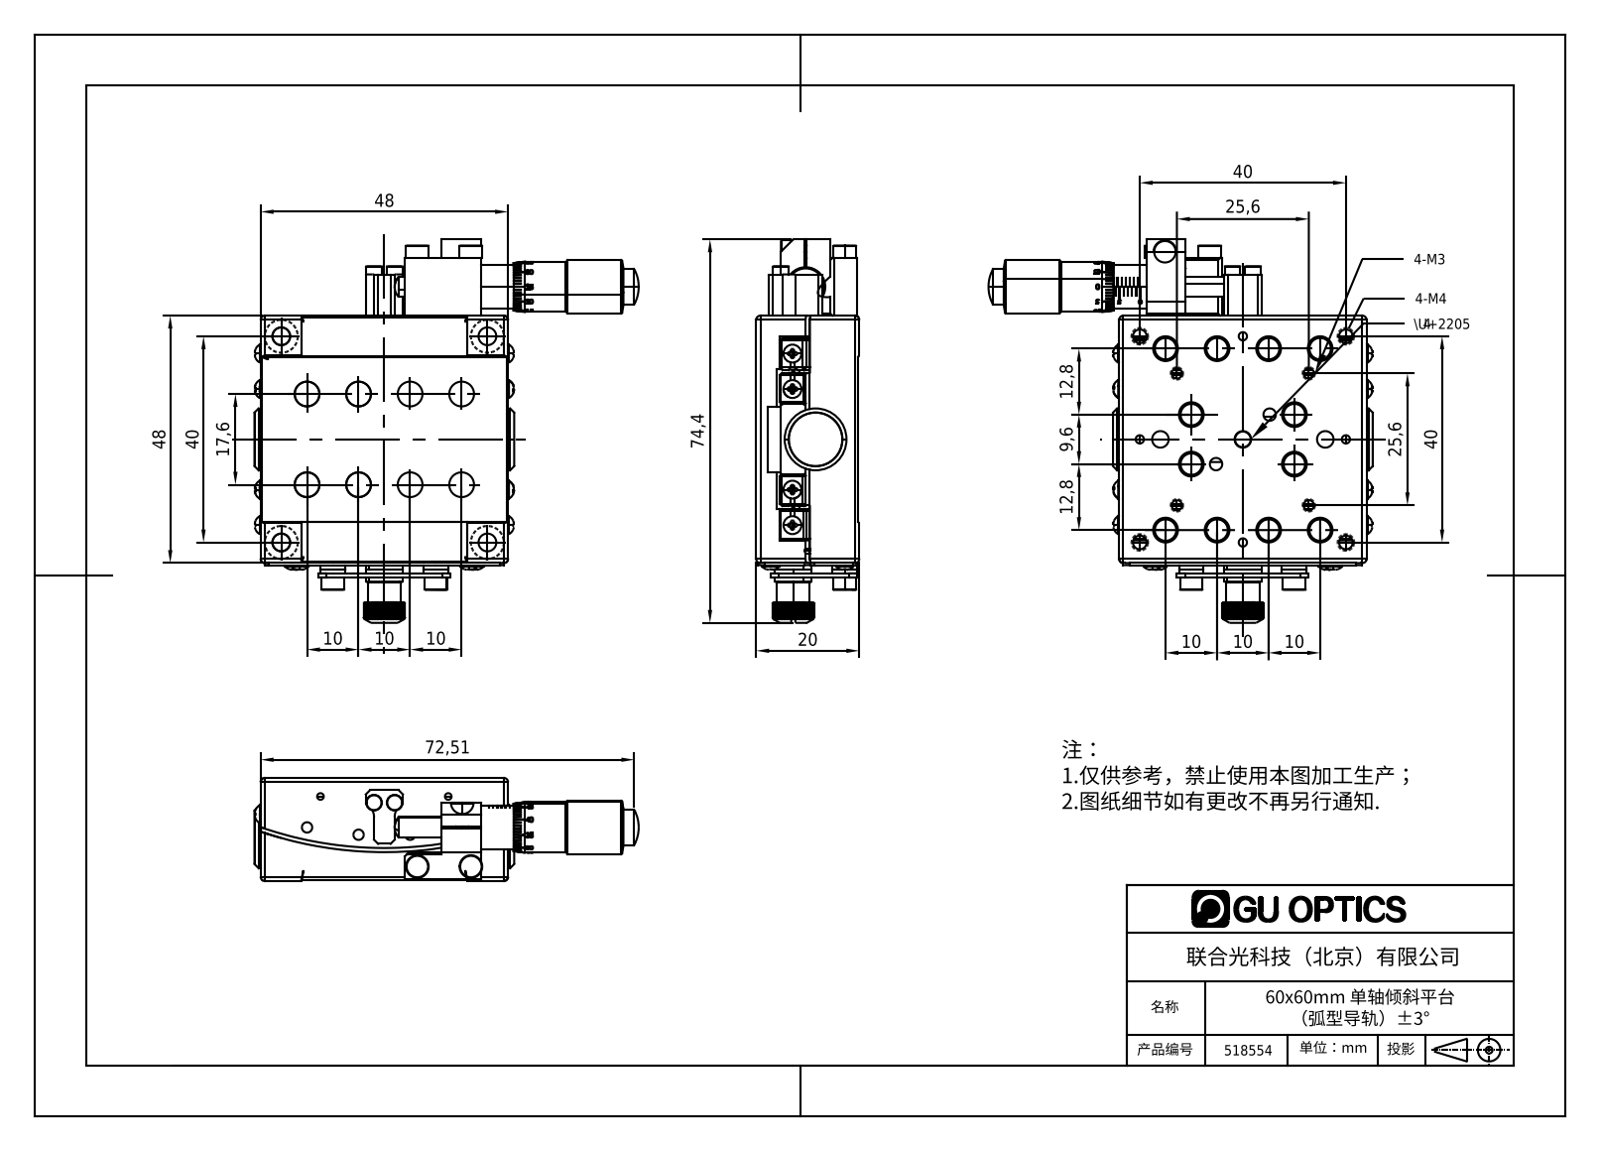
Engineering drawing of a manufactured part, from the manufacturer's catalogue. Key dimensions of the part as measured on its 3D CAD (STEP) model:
Part name (STEP PRODUCT): MXG6-75VM.sldasm-Part-1; MXG6-75VM
STEP written by: SolidWorks 2020 (CONFIG_CONTROL_DESIGN)
Units: millimetres
Bodies: 0 solids, 1538 faces (869 planar, 0 cylindrical, 669 other)
Overall size (bounding box): 93.2 × 93 × 25
Main face-to-face distances: 24.7, 60.5, 0.5, 60, 24.8, 3, 33, 5, 55, 5.5
